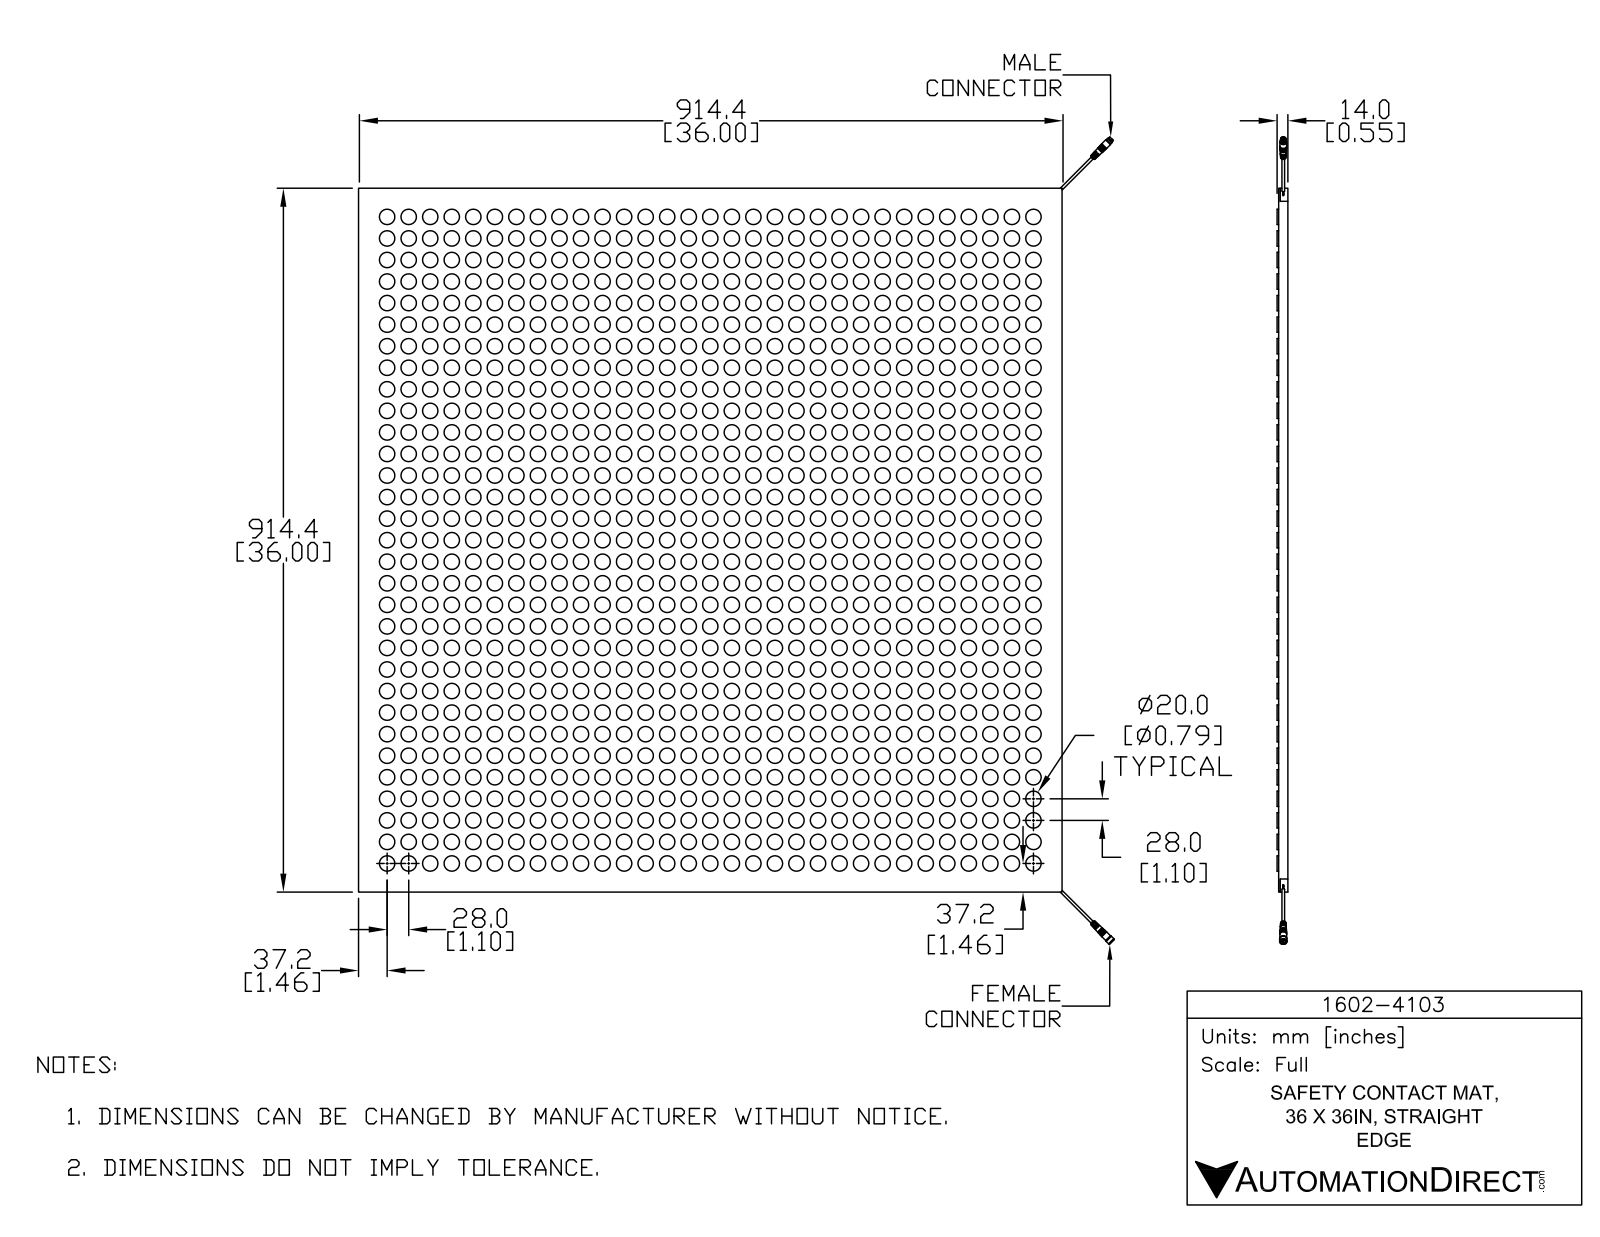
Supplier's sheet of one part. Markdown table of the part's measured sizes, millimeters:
| quantity | value |
| --- | --- |
| part name | 1602-4103_a |
| STEP written by | SolidWorks 2018 (AUTOMOTIVE_DESIGN) |
| units | millimeters |
| bodies | 9 solids, 2175 faces (1077 planar, 1016 cylindrical, 82 other) |
| overall size | 1048.9 × 982.2 × 14 |
| volume | 10 640 000 mm³ |
| surface area | 1 842 000 mm² |
| round holes (diameter × count) | 1.6 × 3, 3.4 × 2, 5.8 × 1, 5.9 × 1, 6.9 × 1, 7.2 × 1 |
| round bosses / shafts (diameter × count) | 20 × 961, 1.2 × 24, 0.8 × 4, 1 × 3, 8.8 × 2, 3.5 × 2, 9.6 × 1, 9 × 1 |
| main face-to-face distances | 12, 2, 14, 914.4, 2.2, 10, 4, 4.4, 1.2, 1 |
| hole center spacings | 1.8, 2.5, 3.5 |
